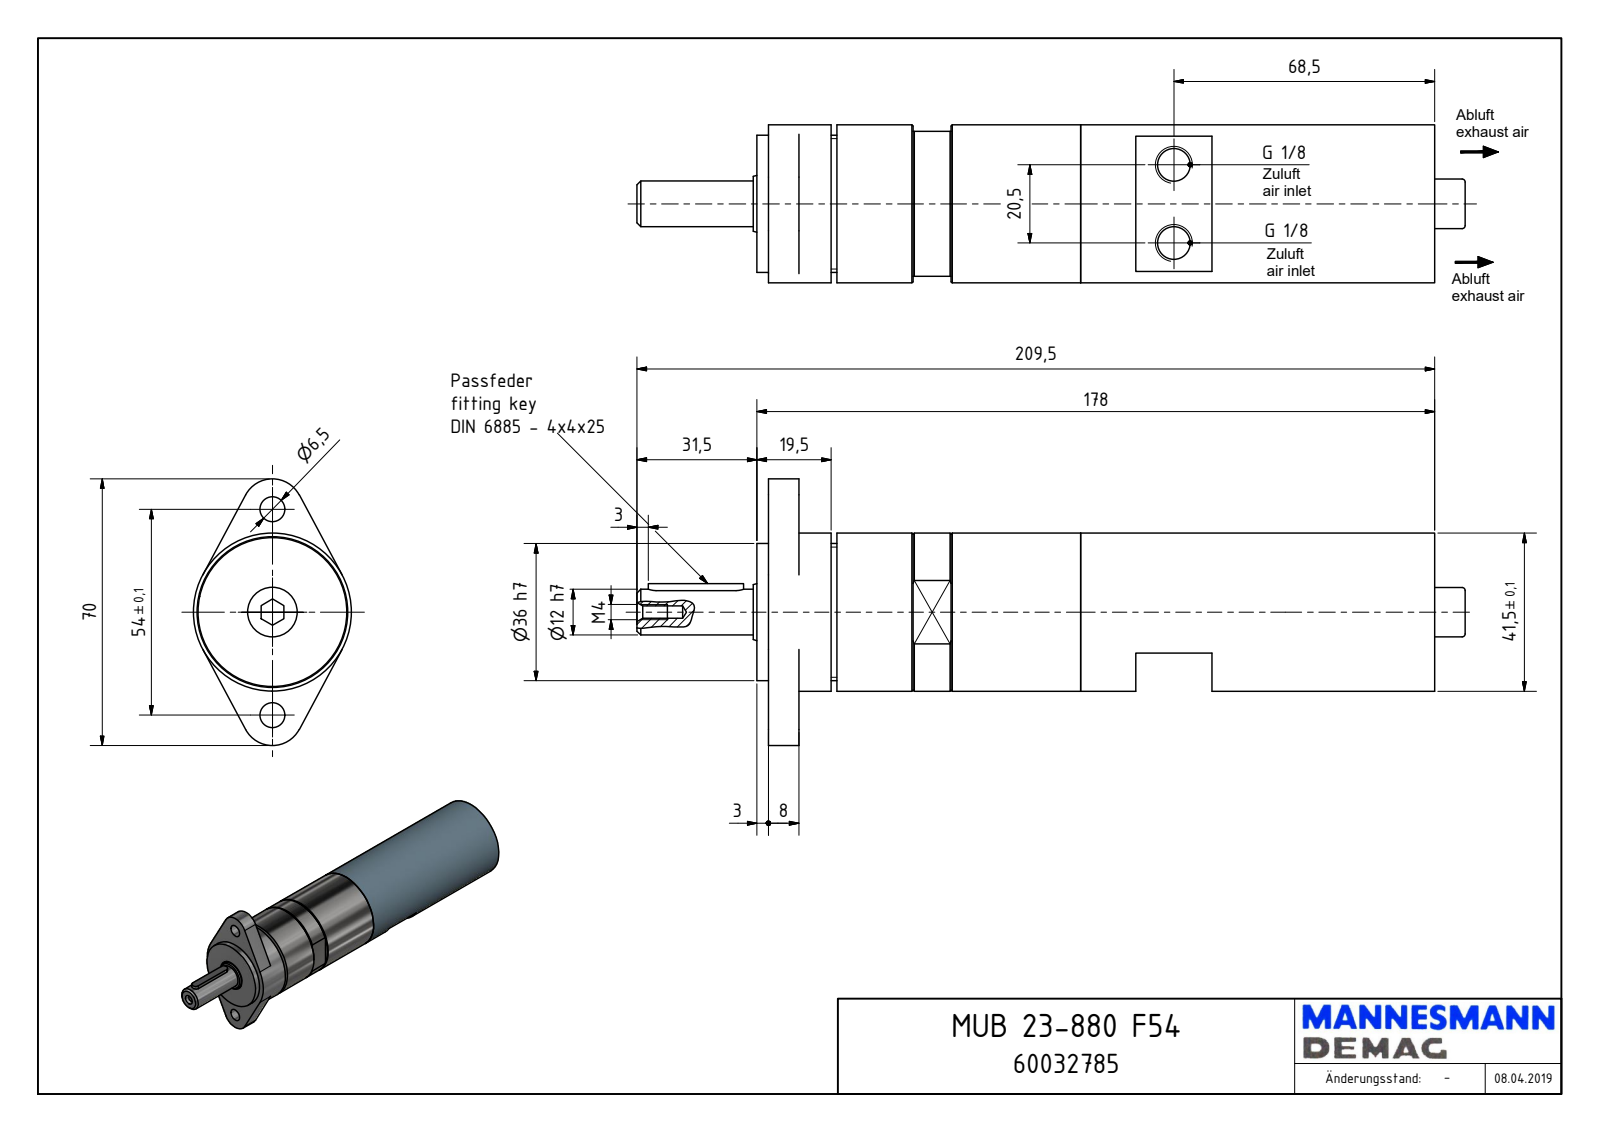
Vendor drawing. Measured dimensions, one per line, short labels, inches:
name: MUB 23-880 F54_60032785
written by: Autodesk Inventor 2018 (AUTOMOTIVE_DESIGN)
unit: in
bodies: 1 solid, 112 faces (53 planar, 47 cylindrical, 12 other)
size: 8.563 × 2.756 × 1.634
volume: 14.74 in³; area: 51.5 in²
holes: 2× ⌀0.256, 2× ⌀0.337, 1× ⌀0.128, 1× ⌀0.335, 1× ⌀0.63, 1× ⌀1.457, 1× ⌀1.496, 1× ⌀1.555
bosses: 1× ⌀1.634, 1× ⌀1.535, 1× ⌀1.417, 1× ⌀1.148, 1× ⌀0.589, 1× ⌀0.512, 1× ⌀0.472, 1× ⌀0.315
rounds: 4× R0.079, 2× R0.098, 2× R0.315
face distances: 6.89, 0.118, 7.008, 0.315, 3.091, 0.433, 6.575, 0.138, 0.925, 3.228
hole spacings: 1.063, 0.807, 2.126
